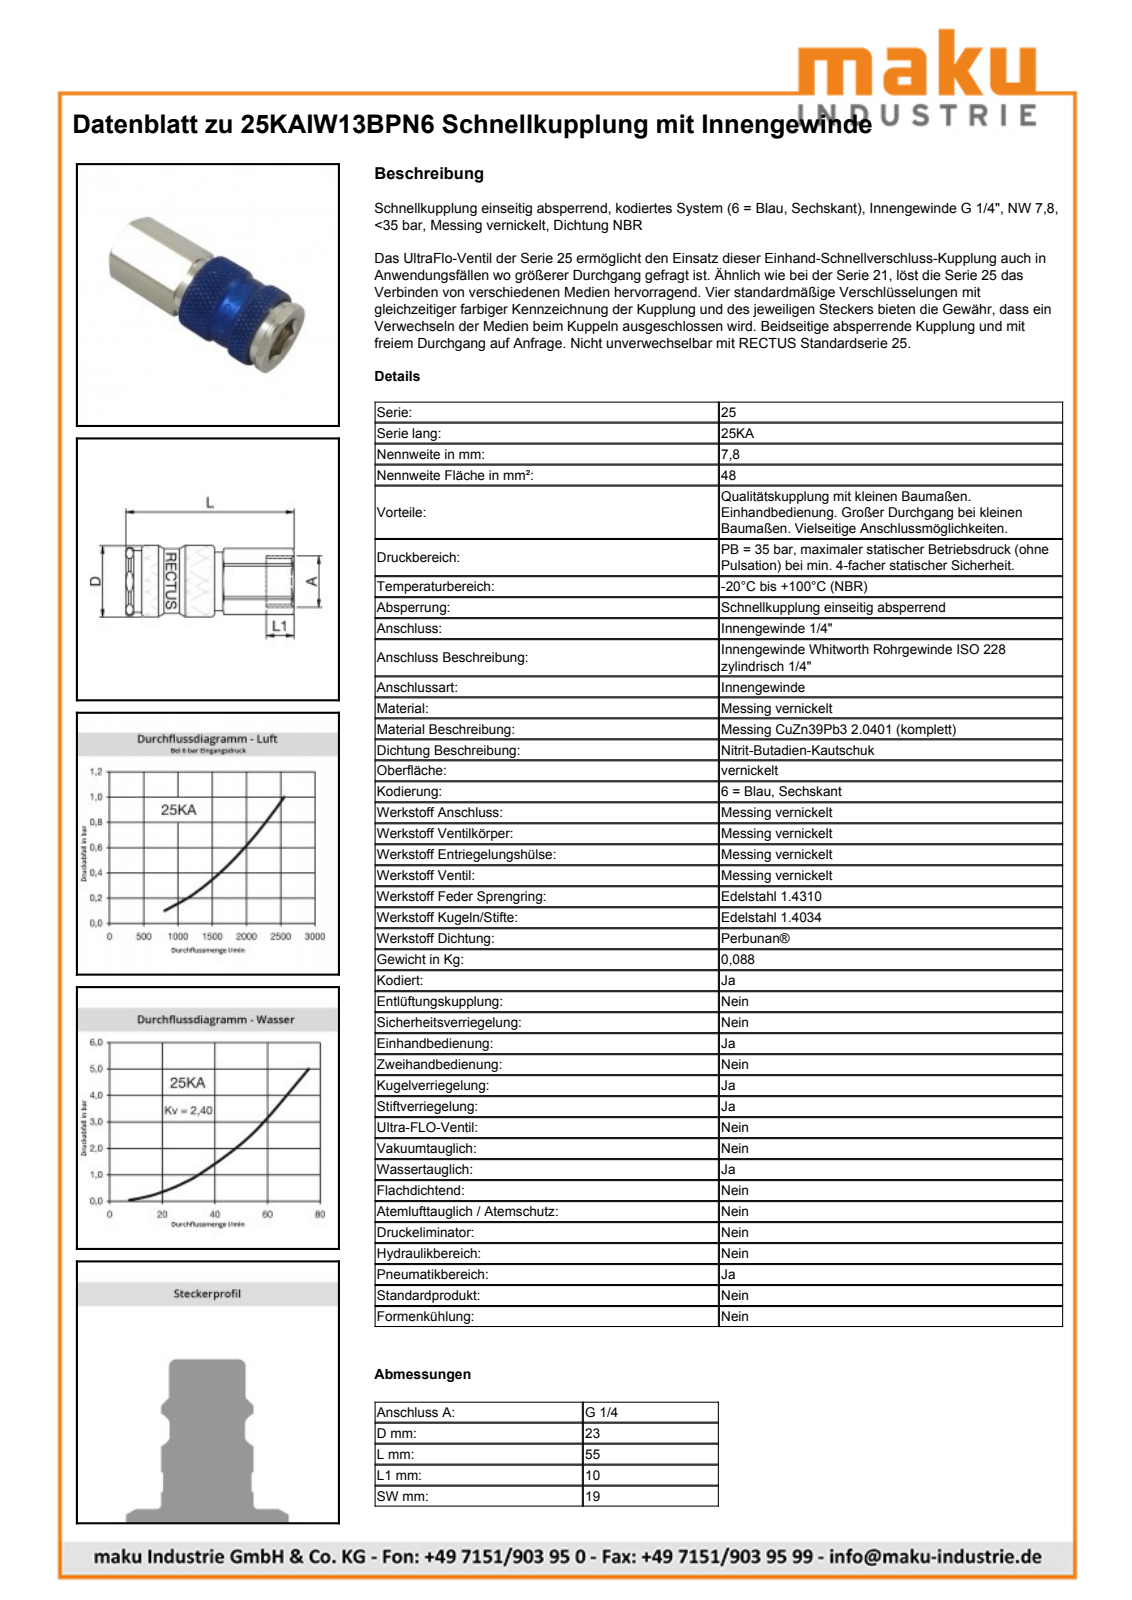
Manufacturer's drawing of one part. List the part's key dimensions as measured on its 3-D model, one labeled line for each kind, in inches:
Part name (STEP PRODUCT): D106609
STEP written by: Autodesk Inventor 2011 (AUTOMOTIVE_DESIGN)
Units: inches
Bodies: 2 solids, 740 faces (253 planar, 87 cylindrical, 400 other)
Overall size (bounding box): 2.185 × 0.911 × 0.911
Volume: 1.036 in³ · Surface area: 13.23 in²
Round holes (diameter × count): ⌀0.451 ×1, ⌀0.551 ×1, ⌀0.594 ×1, ⌀0.63 ×1, ⌀0.679 ×1, ⌀0.762 ×1, ⌀0.789 ×1
Round bosses / shafts (diameter × count): ⌀0.911 ×1, ⌀0.827 ×1, ⌀0.787 ×1, ⌀0.746 ×1, ⌀0.602 ×1, ⌀0.591 ×1, ⌀0.59 ×1
Partial cylindrical surfaces — rounded edges, fillets, slot ends (radius × count): R0.311 ×1, R0.409 ×1, R0.421 ×1, R0.433 ×1
Main face-to-face distances: 0.748, 1.791, 2.185, 0.394, 0.827, 0.965, 0.826, 1.22, 1.13, 0.165
